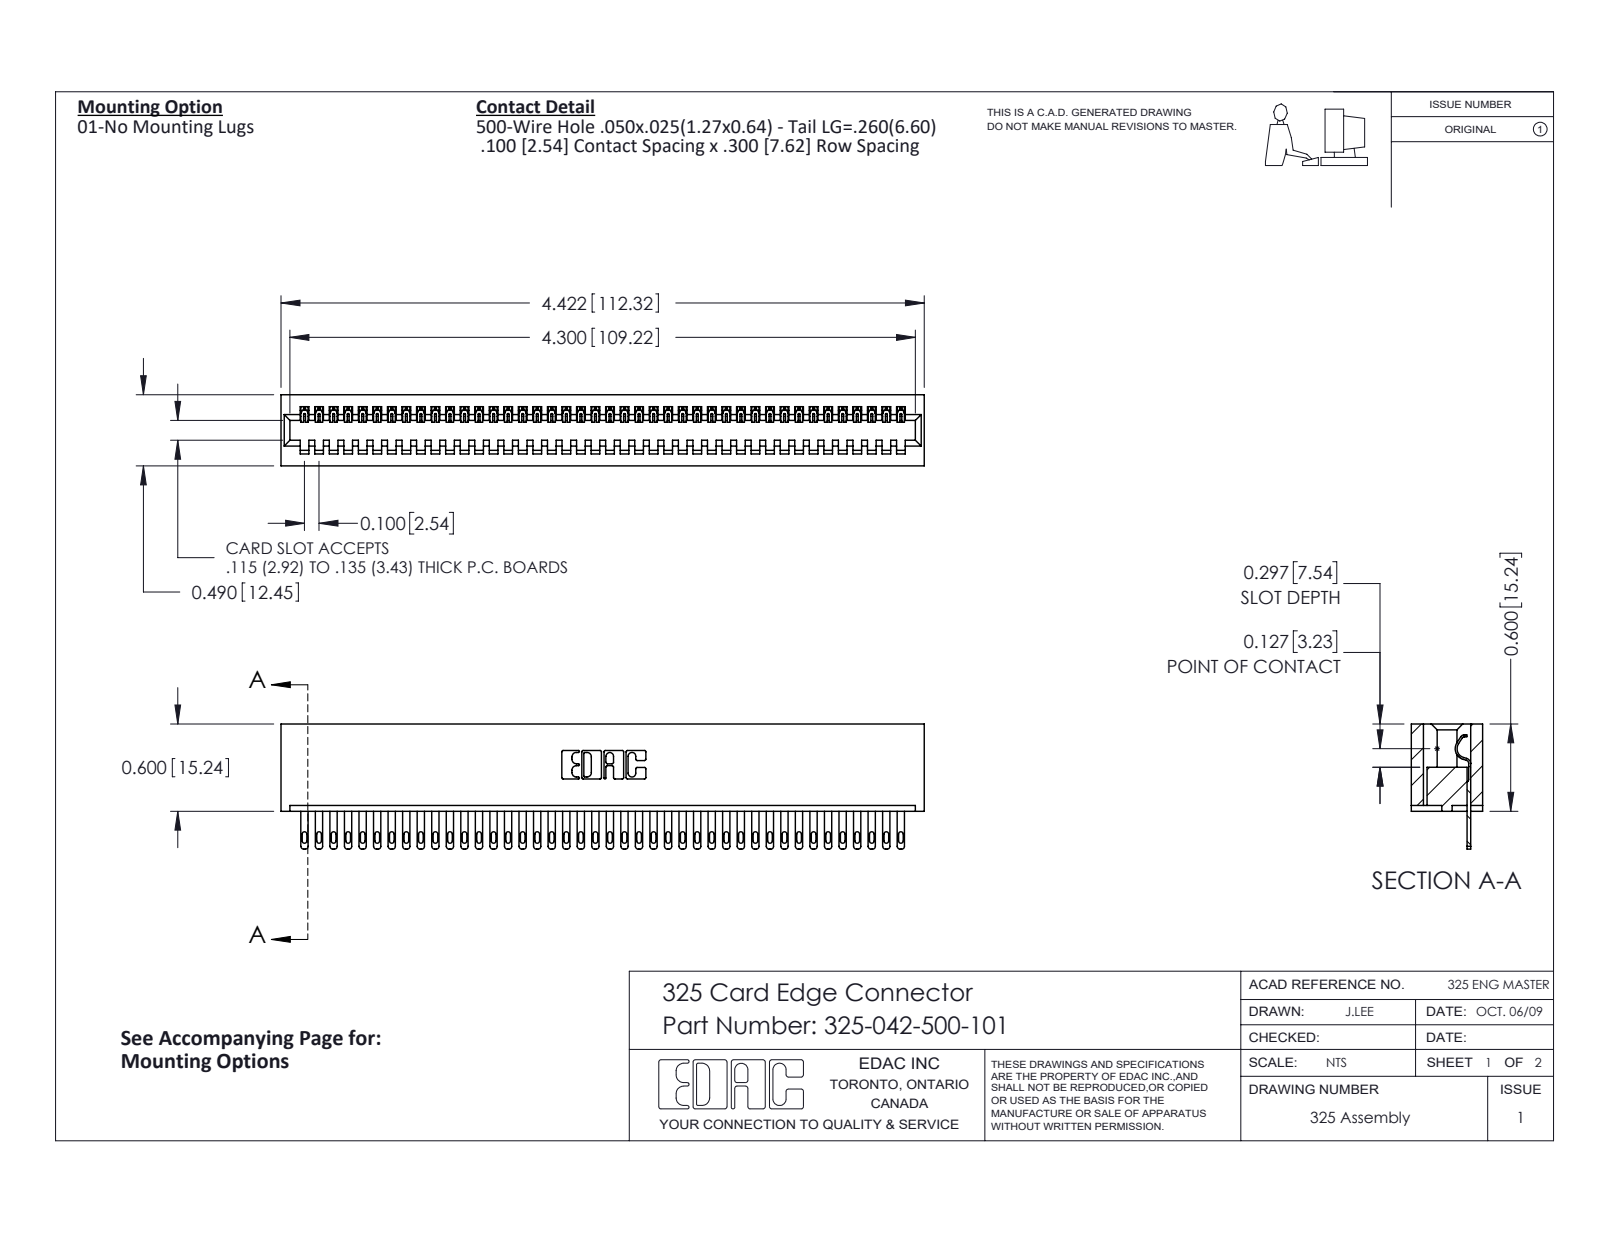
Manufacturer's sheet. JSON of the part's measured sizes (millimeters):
{"part_name": "325-042-500-101; 325 Part_Lugless; 325-292-001_325-293-100", "step_written_by": "SolidWorks 2016 (CONFIG_CONTROL_DESIGN)", "units": "millimeters", "bodies": {"solids": 43, "faces": 2374, "planar": 1578, "cylindrical": 796, "other": 0}, "overall_size": [112.3, 21.8, 12.4], "volume_mm3": 14900, "surface_area_mm2": 16820, "partial_cylinders_radius": [[0.2, 84], [0.4, 84], [0.5, 84], [0.3, 22], [0.2, 6], [0.8, 6], [0.7, 3], [0.4, 1]], "face_to_face_distances": [2.1, 10.3, 7.6, 12.4, 2.7, 9.7, 0.6, 8.3, 14.2, 6.7]}
